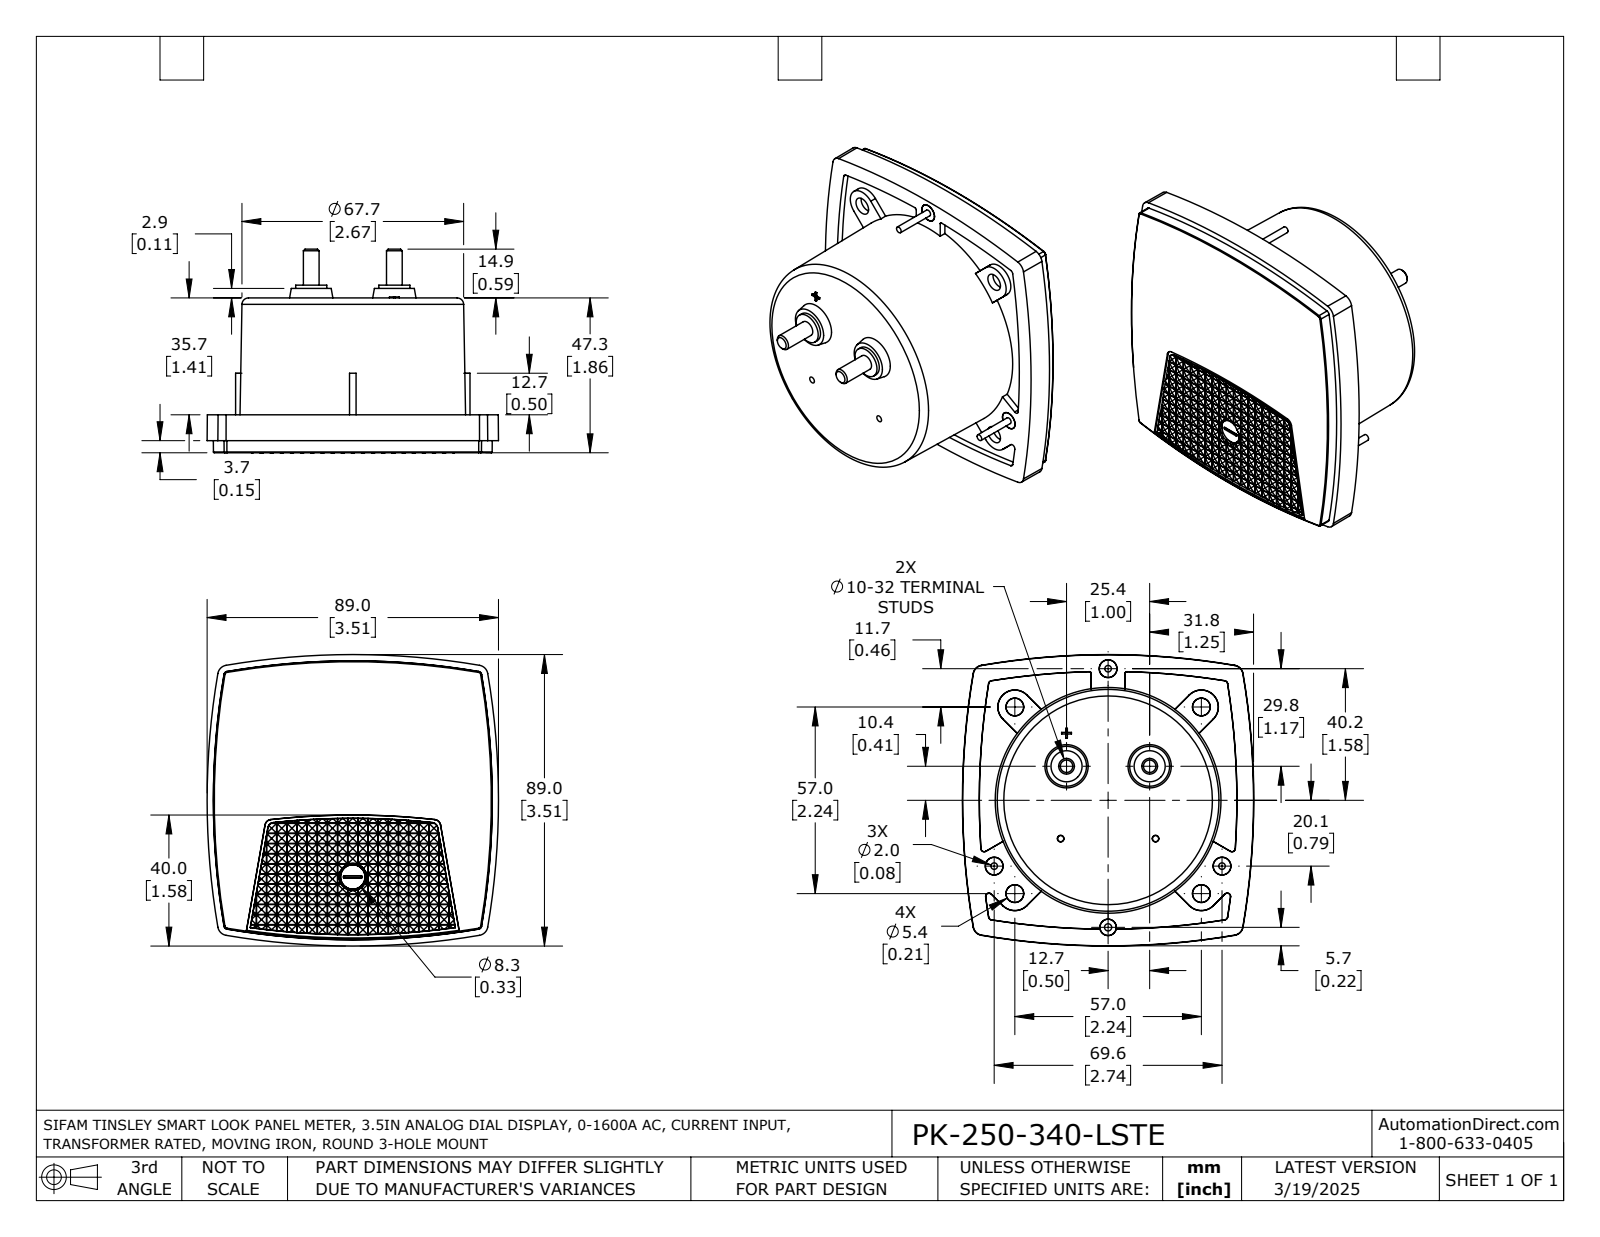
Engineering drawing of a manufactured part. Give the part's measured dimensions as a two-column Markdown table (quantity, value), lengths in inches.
| quantity | value |
| --- | --- |
| part name | PK-250-340-LSTE |
| STEP written by | SolidWorks 2021 (AUTOMOTIVE_DESIGN) |
| units | inches |
| bodies | 1 solid, 1078 faces (950 planar, 23 cylindrical, 105 other) |
| overall size | 3.505 × 3.505 × 2.453 |
| volume | 12.99 in³ |
| surface area | 44.29 in² |
| round holes (diameter × count) | 0.087 × 1 |
| round bosses / shafts (diameter × count) | 0.213 × 3, 0.079 × 3, 0.374 × 2, 0.189 × 2 |
| partial cylindrical surfaces (radius × count) | 8.961 × 1 |
| main face-to-face distances | 1.862, 1.406, 0.457, 0.079, 1.484, 0.378, 0.024, 0.096, 0.072, 0.12 |
